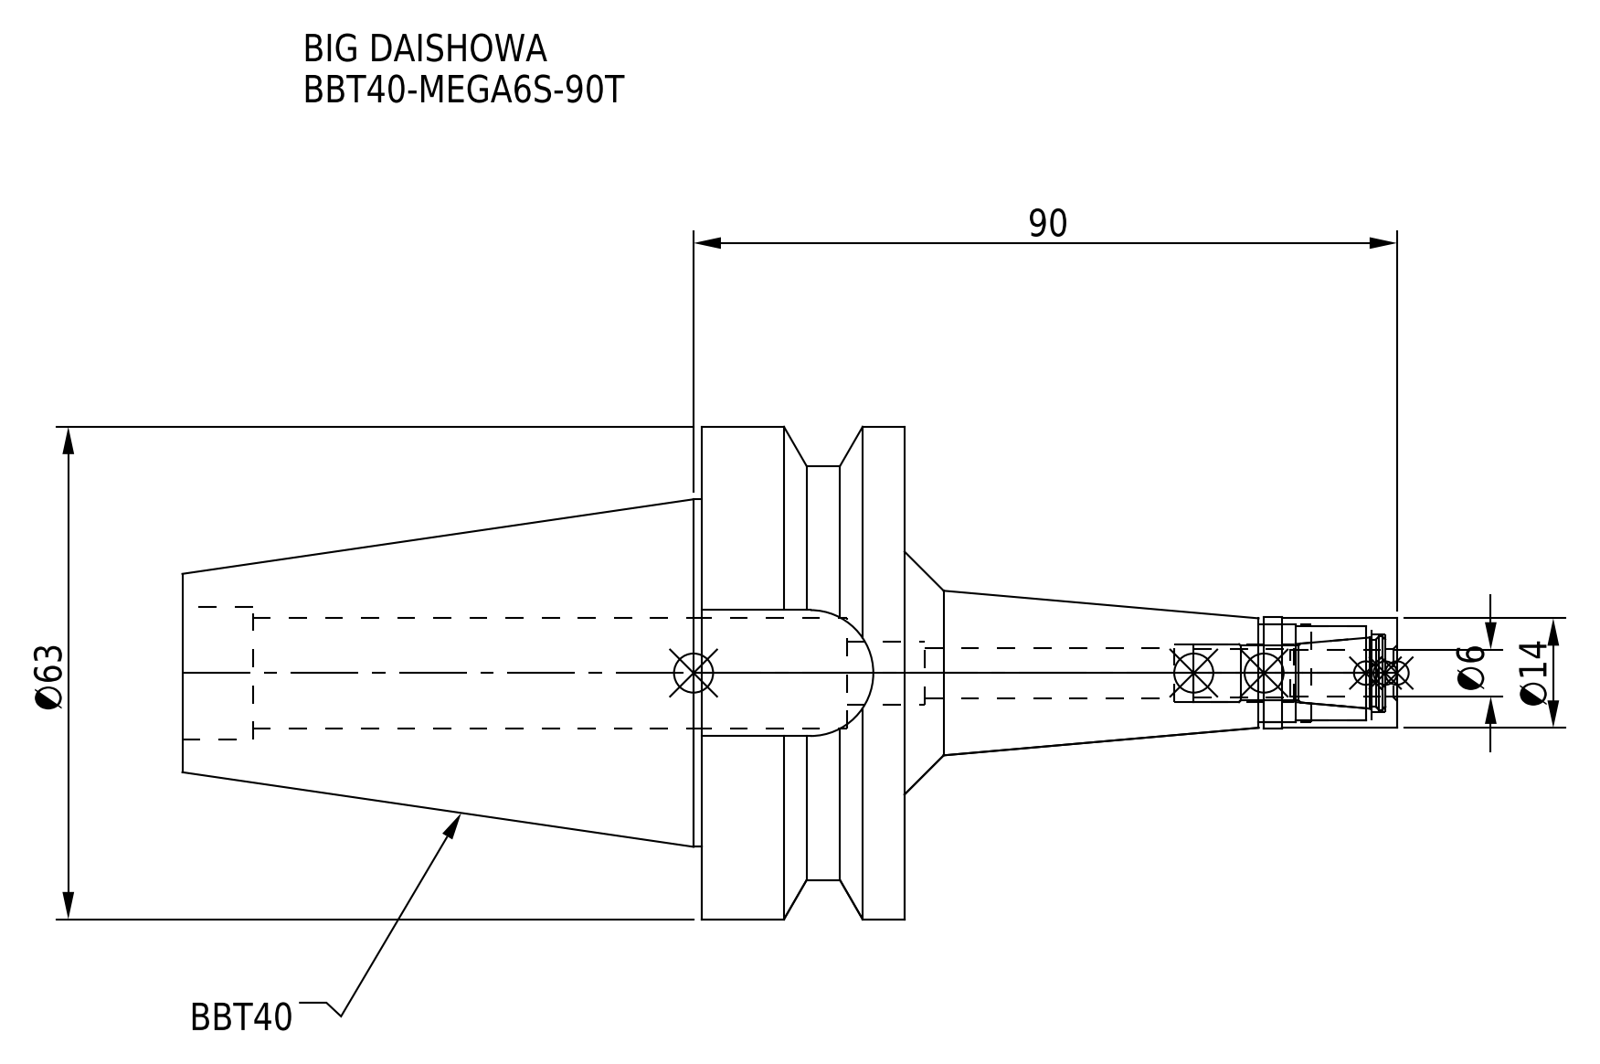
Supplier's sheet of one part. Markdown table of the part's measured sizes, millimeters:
| quantity | value |
| --- | --- |
| part name | MGN6S_1.stp; BBT40MS06090T-060_ASM.stp; BBT40-MEGA6S-90T; DXF_TEMP_ASSY_ASM_4_ASM.stp (+3 more) |
| STEP written by | SolidWorks 2019 (CONFIG_CONTROL_DESIGN) |
| units | millimeters |
| bodies | 2 solids, 74 faces (22 planar, 38 cylindrical, 14 other) |
| overall size | 155.4 × 63 × 63 |
| volume | 133 810 mm³ |
| surface area | 28 429 mm² |
| round holes (diameter × count) | 6.1 × 1, 6.4 × 1, 7.4 × 1, 8 × 1, 10 × 1, 12 × 1, 12.5 × 1, 14.2 × 1, 17 × 1 |
| round bosses / shafts (diameter × count) | 63 × 1, 53 × 1, 44.45 × 1, 14.3 × 1, 14 × 1 |
| partial cylindrical surfaces (radius × count) | 8.05 × 1 |
| main face-to-face distances | 26, 66.4, 45, 92.4, 16.1, 85, 63, 89, 155.4, 70.4 |
